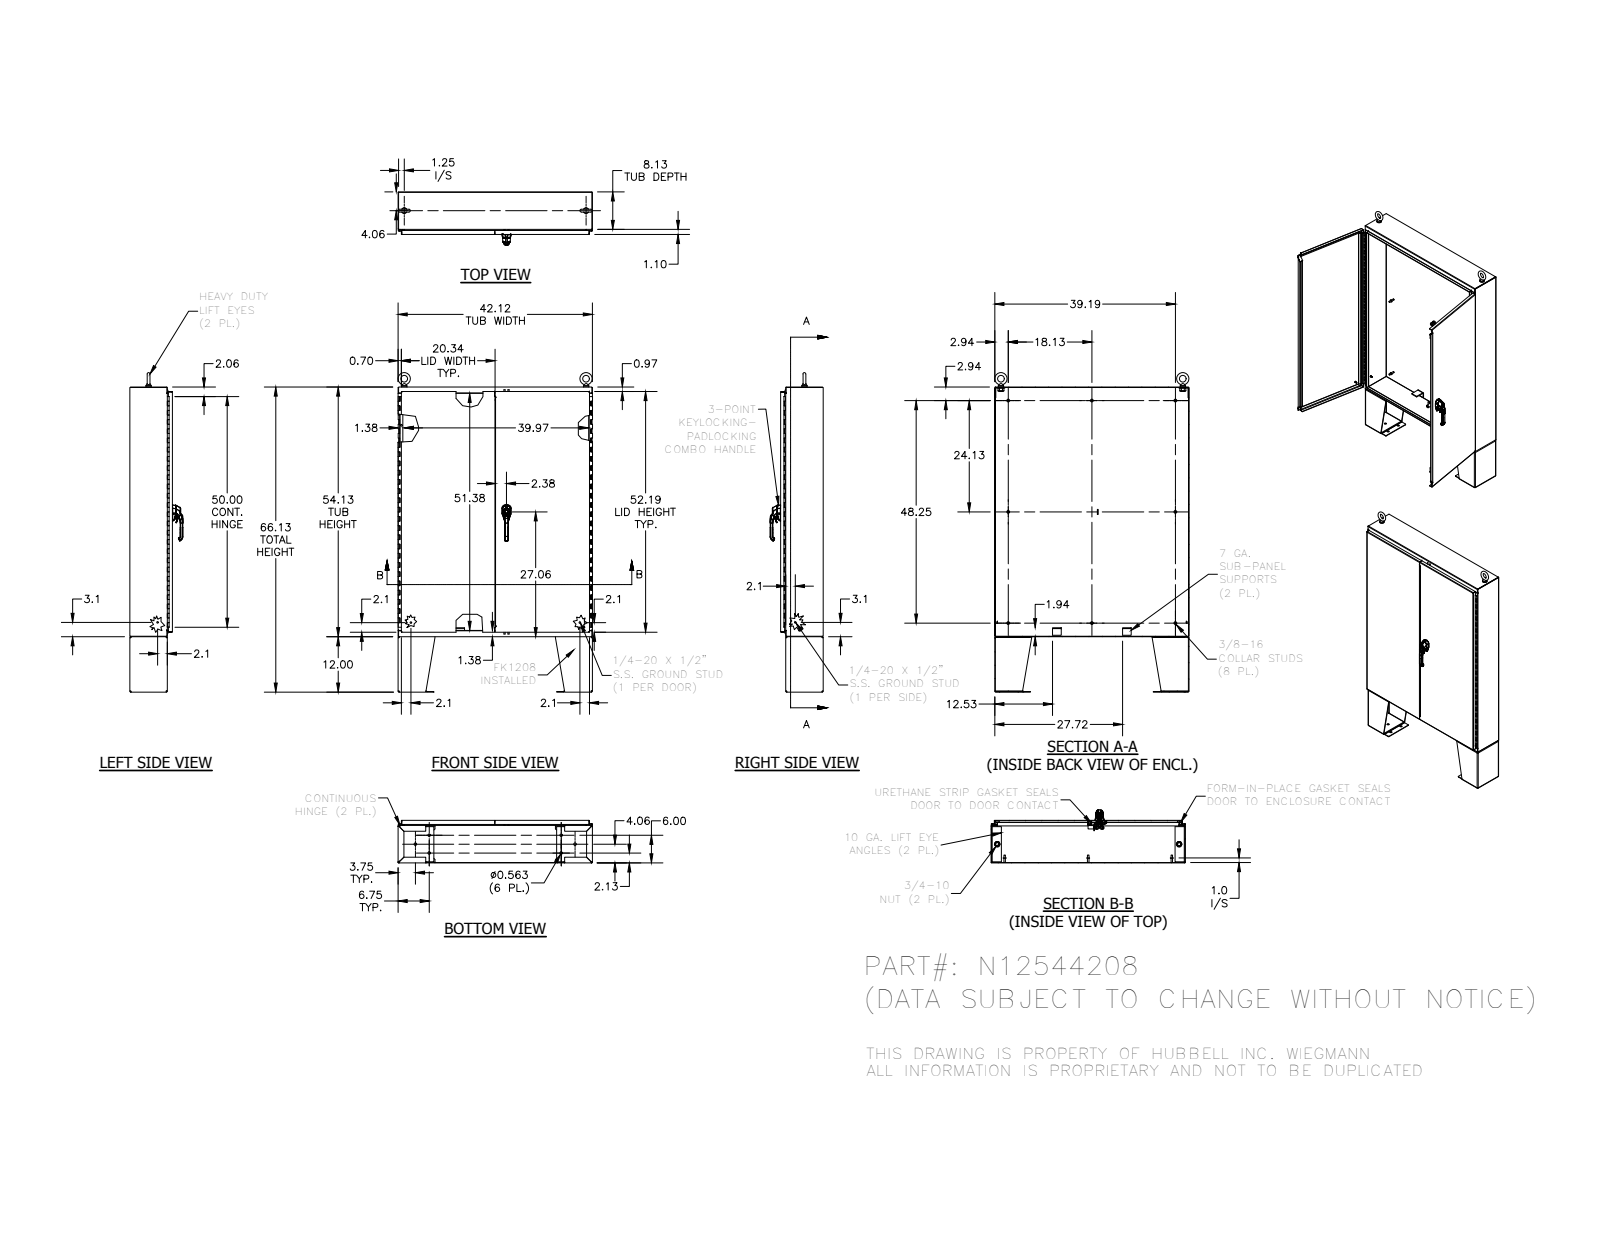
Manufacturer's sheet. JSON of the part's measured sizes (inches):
{"part_name": "N12544208", "step_written_by": "SolidWorks 2018 (AUTOMOTIVE_DESIGN)", "units": "inches", "bodies": {"solids": 69, "faces": 1676, "planar": 862, "cylindrical": 516, "other": 298}, "overall_size": [69.248, 42.169, 11.405], "volume_in3": 812.5, "surface_area_in2": 16075, "round_holes": [[0.563, 18], [0.277, 8], [0.2, 4], [0.28, 3], [0.18, 2], [0.241, 2], [0.25, 2], [0.252, 2], [0.4, 2], [0.45, 2], [0.642, 2], [0.813, 2]], "round_bosses_or_shafts": [[0.33, 10], [0.625, 5], [0.625, 3], [0.337, 3], [0.25, 3], [1.25, 2], [1.12, 2], [1, 2]], "partial_cylinders_radius": [[0.031, 28], [0.125, 19], [0.05, 18], [0.094, 17], [0.025, 16], [0.219, 16], [0.03, 11], [0.067, 8]], "face_to_face_distances": [0.094, 9.133, 9.039, 9.227, 54.031, 0.093, 42.125, 0.125, 42.031, 42.031], "hole_center_spacings": [1.928, 2.041, 3.559, 3.571, 4.685, 5, 6.064, 6.503]}
